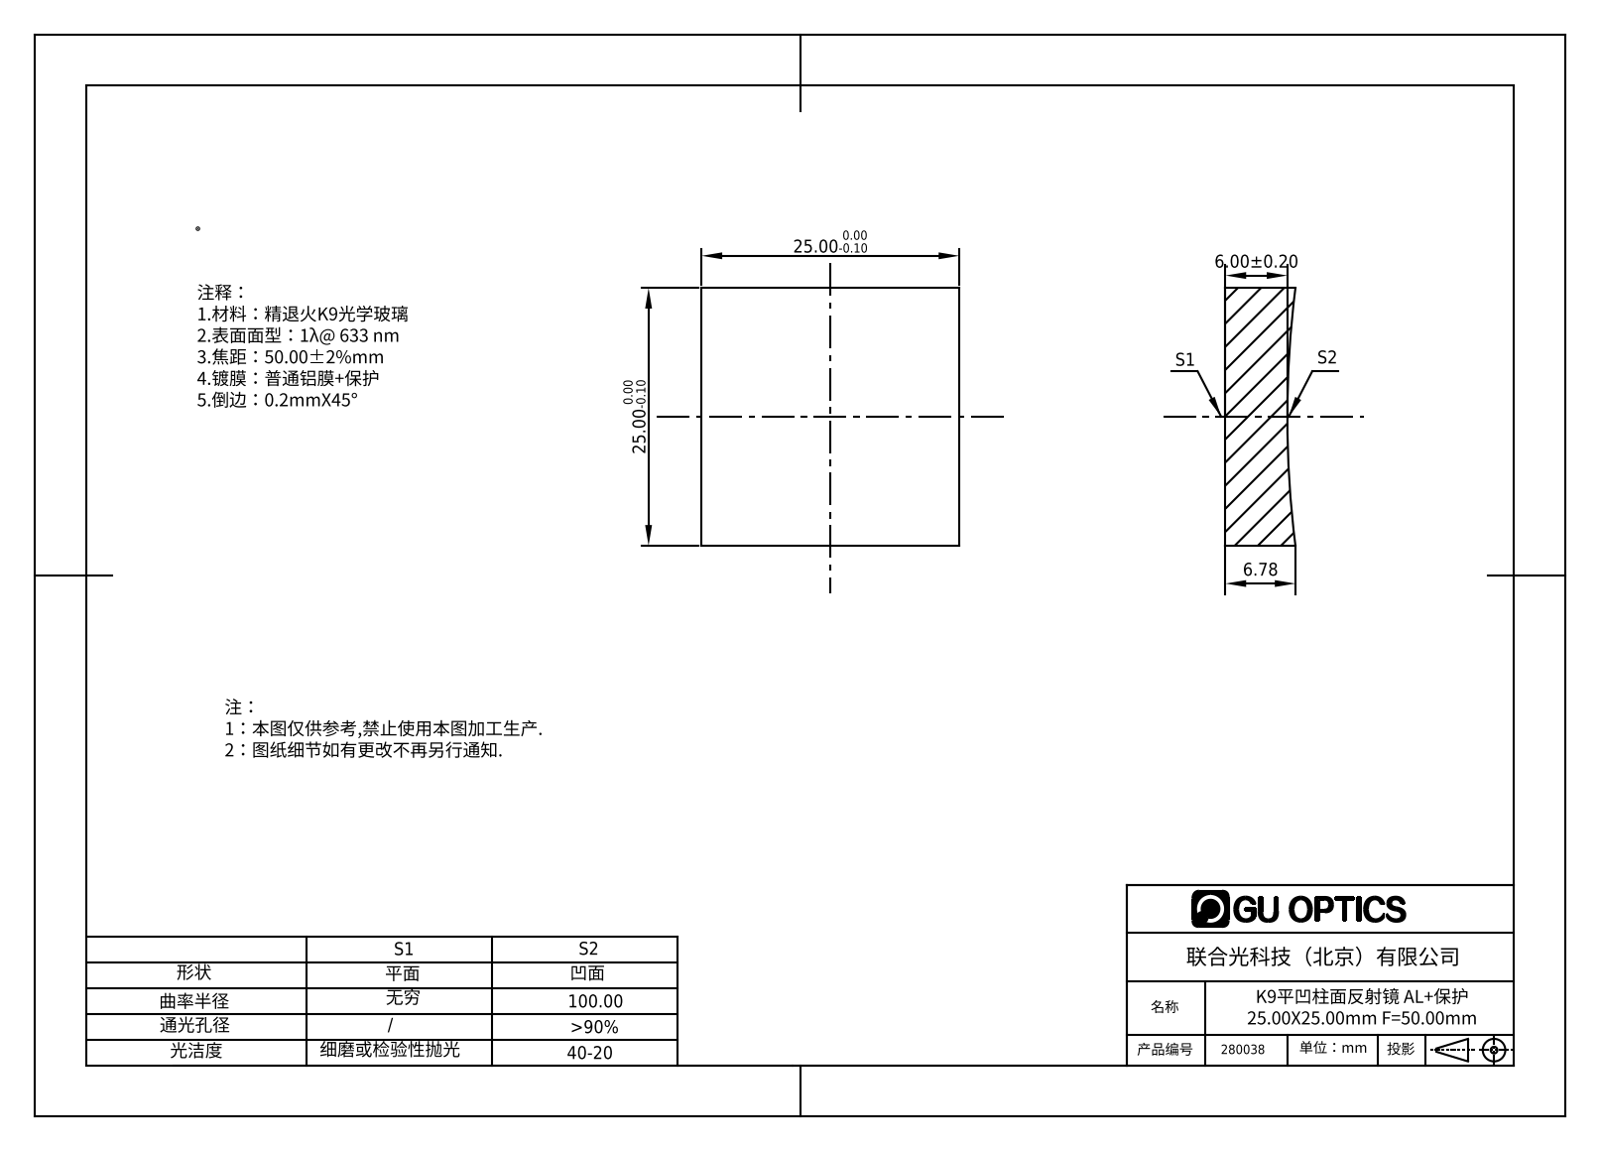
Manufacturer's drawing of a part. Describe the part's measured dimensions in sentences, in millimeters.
The part is named "280016". Its 3-D file was written by "SolidWorks 2016 (AUTOMOTIVE_DESIGN)". It is 1 solid with 7 faces: 5 planar, 2 cylindrical and 0 other. Overall it measures 25 by 25 by 6.78 millimeters. Its volume is 3 913 cubic millimeters and its surface area 1 904 square millimeters. Partial cylindrical surfaces (rounded edges, fillets, slot ends): 1 of radius 100. The main face-to-face distances are 25.
